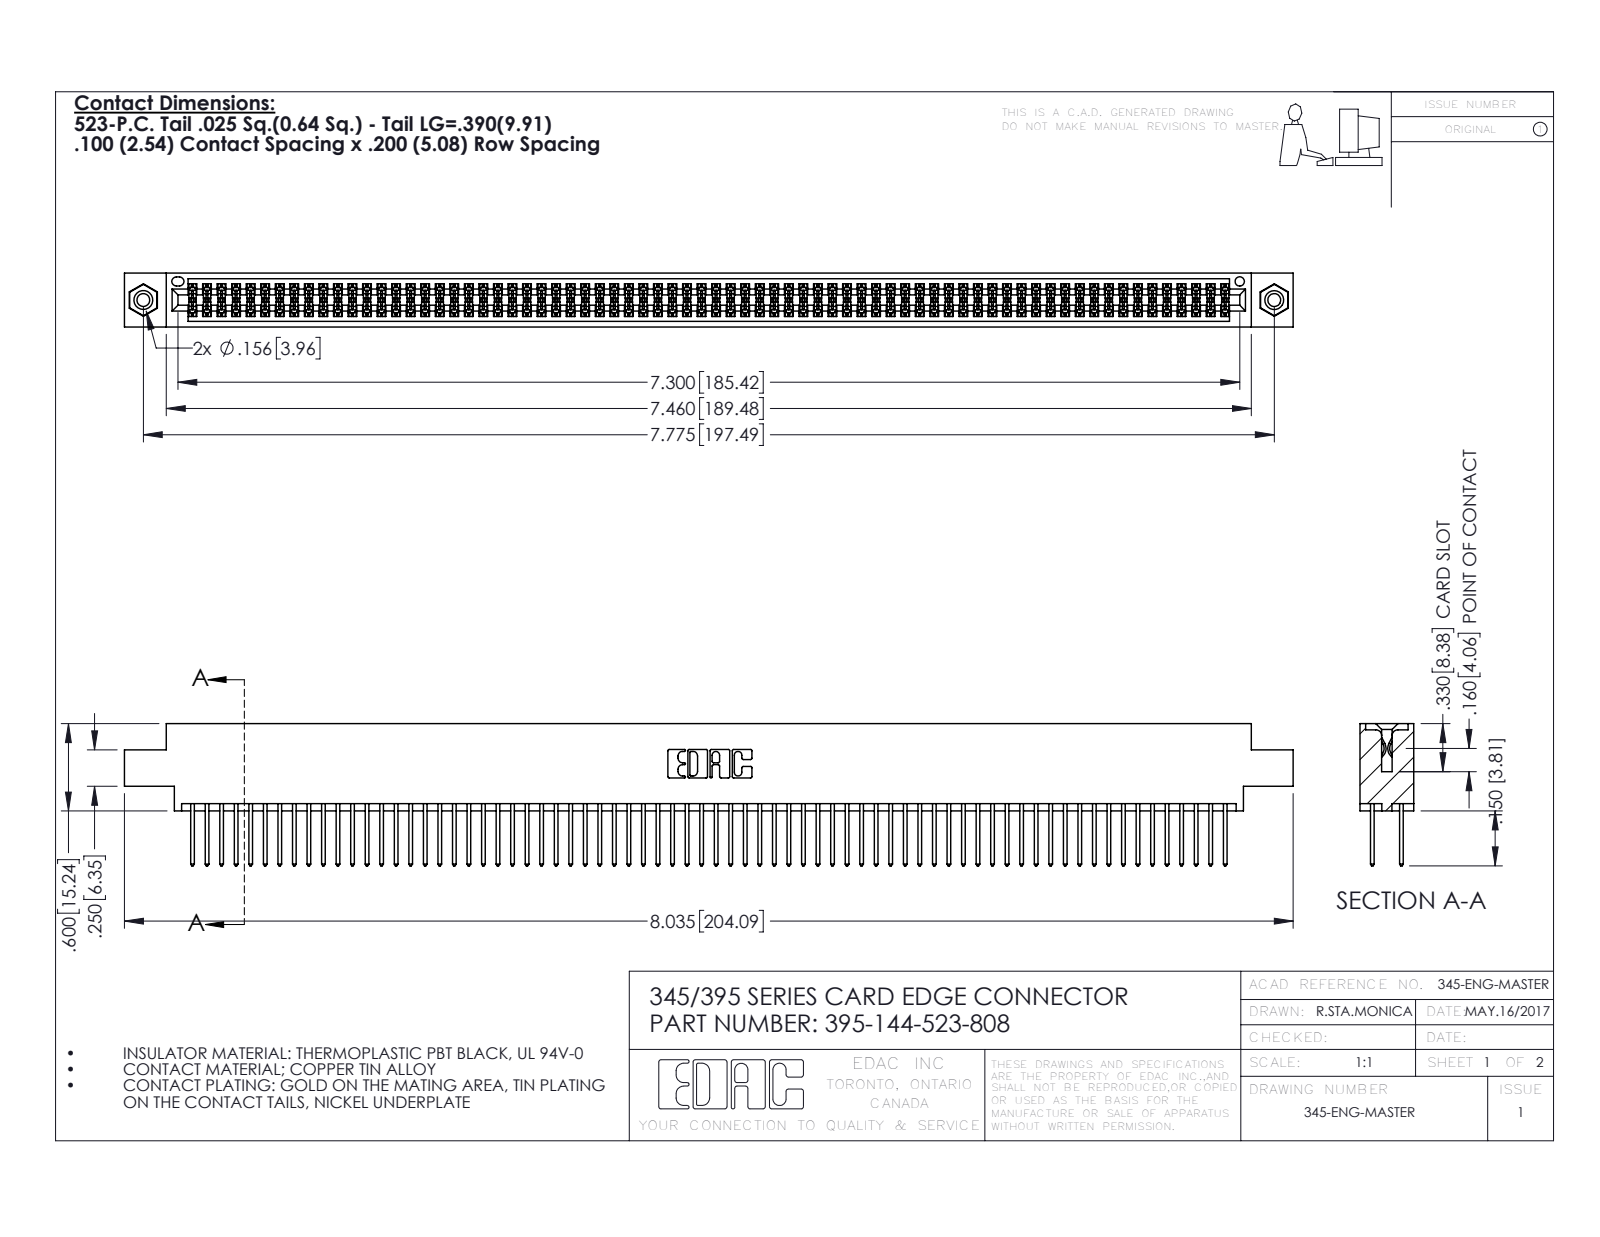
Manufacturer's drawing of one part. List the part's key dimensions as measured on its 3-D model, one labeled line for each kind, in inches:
Part name (STEP PRODUCT): 395-144-523-808; 345 Part_0.170 Offset - 0.156 Dia-TI; 345-292-001_345-293-123; 345-250-001_345-250-003-102
STEP written by: SolidWorks 2016 (CONFIG_CONTROL_DESIGN)
Units: inches
Bodies: 147 solids, 7390 faces (4868 planar, 2506 cylindrical, 16 other)
Overall size (bounding box): 8.035 × 0.977 × 0.37
Volume: 1.238 in³ · Surface area: 49.66 in²
Round holes (diameter × count): ⌀0.089 ×2, ⌀0.125 ×2, ⌀0.156 ×2, ⌀0.064 ×1
Round bosses / shafts (diameter × count): ⌀0.155 ×2
Partial cylindrical surfaces — rounded edges, fillets, slot ends (radius × count): R0.006 ×216, R0.01 ×144, R0.01 ×22, R0.007 ×6, R0.031 ×6, R0.026 ×3, R0.014 ×2, R0.019 ×2
Main face-to-face distances: 0.072, 0.298, 0.2, 0.098, 0.272, 0.025, 0.37, 0.225, 0.175, 0.149
Hole centre spacings: 0.27, 7.539, 7.775
